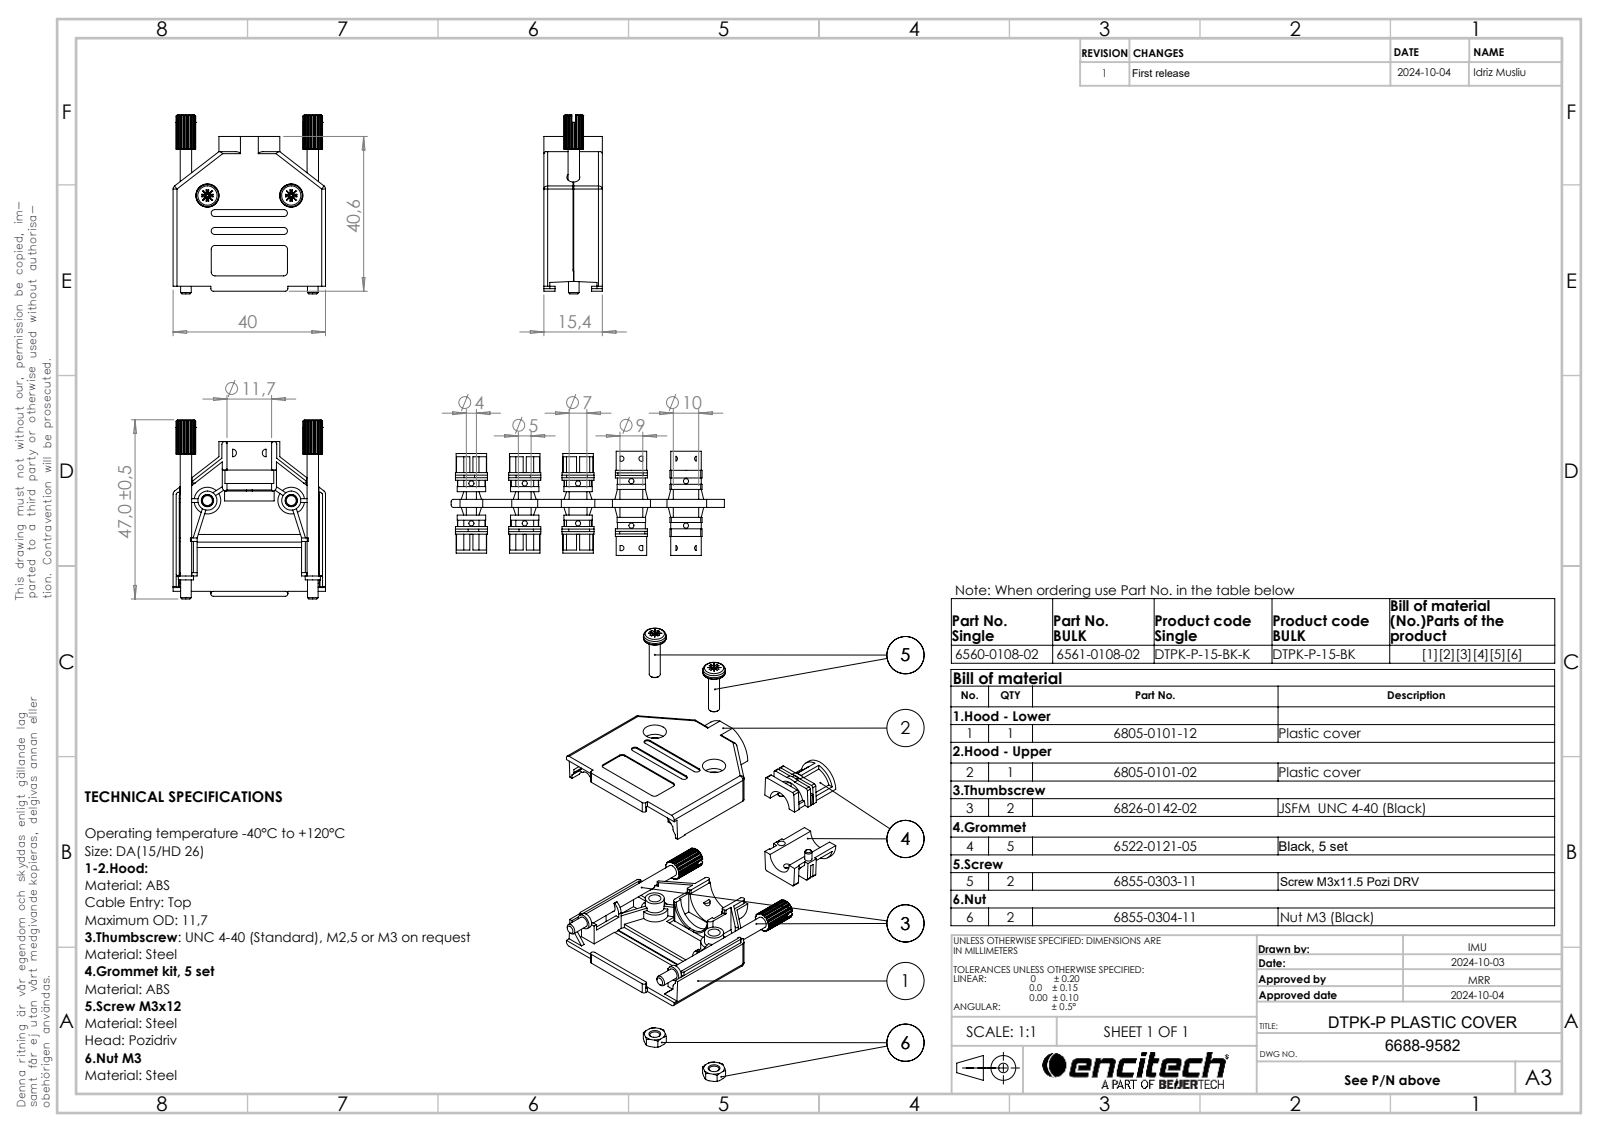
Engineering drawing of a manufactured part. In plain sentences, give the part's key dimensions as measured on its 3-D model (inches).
The part is named "6688-9582; 6522-0121-05 (7mm); 6805-0101-12; 6826-0142-02 (+3 more)". Its 3-D file was written by "SolidWorks 2021 (AUTOMOTIVE_DESIGN)". It is 10 solids with 913 faces: 564 planar, 253 cylindrical and 96 other. Overall it measures 1.85 by 1.575 by 0.604 inches. Its volume is 0.561 cubic inches and its surface area 21.68 square inches. Round holes: 3 of diameter 0.079, 2 of diameter 0.102, 2 of diameter 0.126, 2 of diameter 0.24, 1 of diameter 0.276. Round bosses or shafts: 2 of diameter 0.276, 2 of diameter 0.197, 2 of diameter 0.157, 2 of diameter 0.118, 2 of diameter 0.114, 2 of diameter 0.11, 2 of diameter 0.075, 1 of diameter 0.457. Partial cylindrical surfaces (rounded edges, fillets, slot ends): 18 of radius 0.039, 10 of radius 0.02, 8 of radius 0.004, 8 of radius 0.012, 4 of radius 0.016, 4 of radius 0.03, 4 of radius 0.035, 4 of radius 0.063. The main face-to-face distances are 0.604, 0.055, 0.063, 0.543, 0.488, 0.549, 0.061, 0.039, 1.512, 0.593. The hole center spacings are 0.225, 0.338, 0.453, 0.675, 0.394, 0.866.
